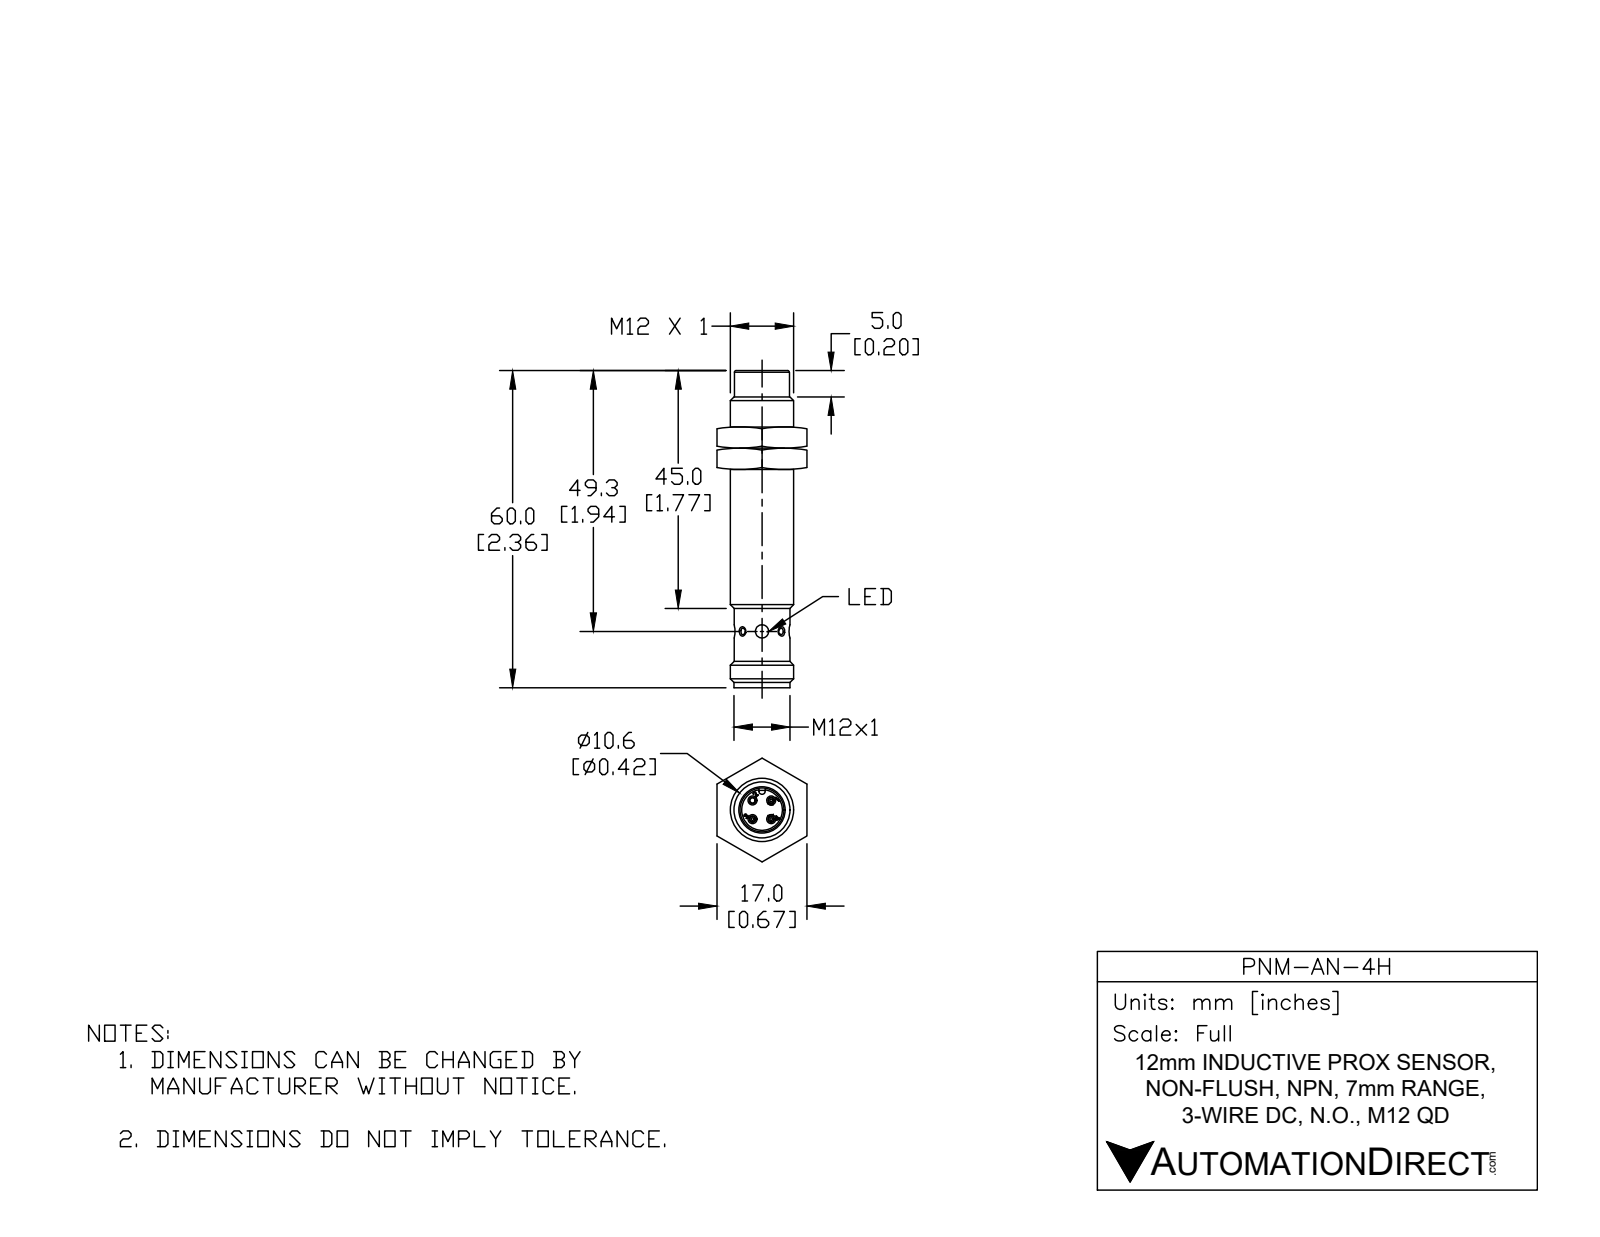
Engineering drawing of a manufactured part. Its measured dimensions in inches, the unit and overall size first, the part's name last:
Units: inches
Overall size (bounding box): 2.362 × 0.472 × 0.472
Round holes (diameter × count): ⌀0.043 ×3, ⌀0.04 ×2, ⌀0.098 ×2, ⌀0.038 ×1, ⌀0.04 ×1, ⌀0.327 ×1, ⌀0.394 ×1, ⌀0.401 ×1
Round bosses / shafts (diameter × count): ⌀0.039 ×9, ⌀0.472 ×1, ⌀0.417 ×1, ⌀0.415 ×1, ⌀0.4 ×1, ⌀0.392 ×1, ⌀0.39 ×1, ⌀0.376 ×1
Partial cylindrical surfaces — rounded edges, fillets, slot ends (radius × count): R0.004 ×36, R0.024 ×1, R0.031 ×1, R0.161 ×1
Main face-to-face distances: 0.039, 1.87, 1.831, 0.018, 0.022, 1.852, 2.323, 0.142, 2.012, 1.994
Hole centre spacings: 0.098, 0.139, 0.197
Volume: 0.35 in³ · Surface area: 10.25 in²
Bodies: 1 solid, 479 faces (119 planar, 134 cylindrical, 226 other)
Part name (STEP PRODUCT): PNM-AN-4H
STEP written by: SolidWorks 2017 (AUTOMOTIVE_DESIGN)
